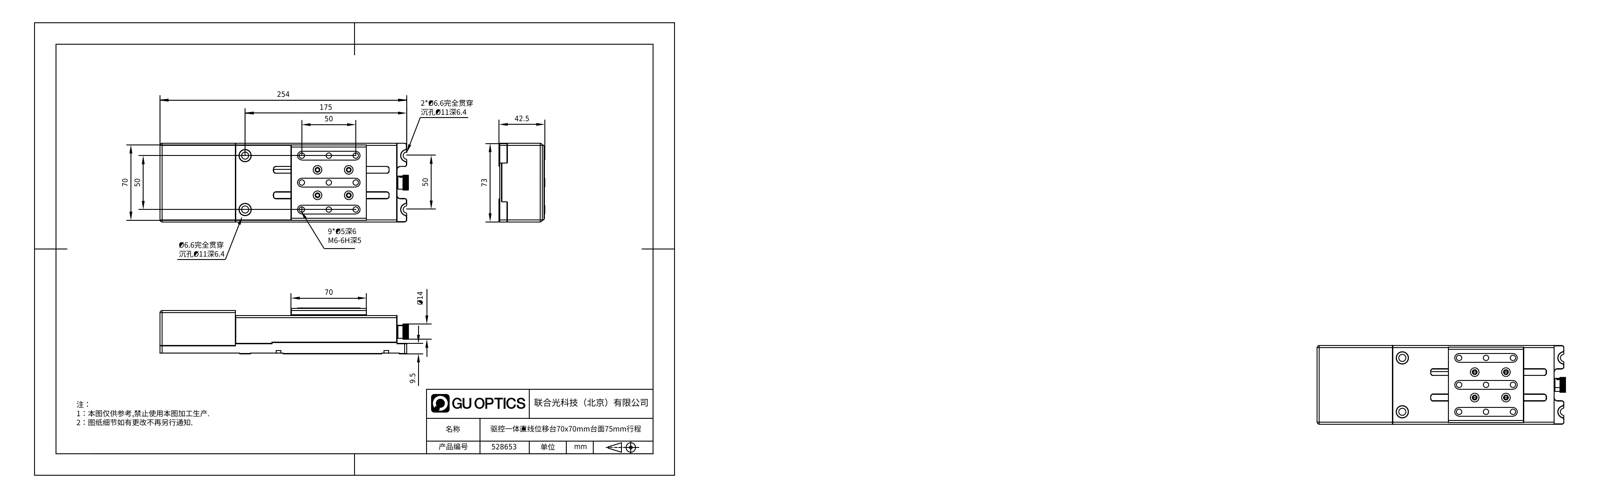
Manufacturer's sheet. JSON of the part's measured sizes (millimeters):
{"part_name": "528653", "step_written_by": "SolidWorks 2020 (CONFIG_CONTROL_DESIGN)", "units": "millimeters", "bodies": {"solids": 45, "faces": 2313, "planar": 1187, "cylindrical": 740, "other": 386}, "overall_size": [255.5, 73, 42.5], "volume_mm3": 457306, "surface_area_mm2": 197599, "round_holes": [[2.4, 42], [1.6, 26], [4.4, 25], [4.2, 18], [2.5, 17], [1.57, 16], [3.4, 16], [6.5, 12], [5, 10], [3.3, 6], [1.57, 4], [2, 4]], "round_bosses_or_shafts": [[2.2, 4], [2, 4], [22, 1], [12, 1]], "partial_cylinders_radius": [[2, 31], [1, 25], [4, 6], [0.7, 4], [1.3, 4], [0.3, 2], [0.4, 2], [3, 2]], "face_to_face_distances": [2, 4, 1, 33, 35, 25, 26, 2.5, 7, 0.5], "hole_center_spacings": [9, 25, 18.26, 35.36, 55.9, 8, 12, 14.42]}
